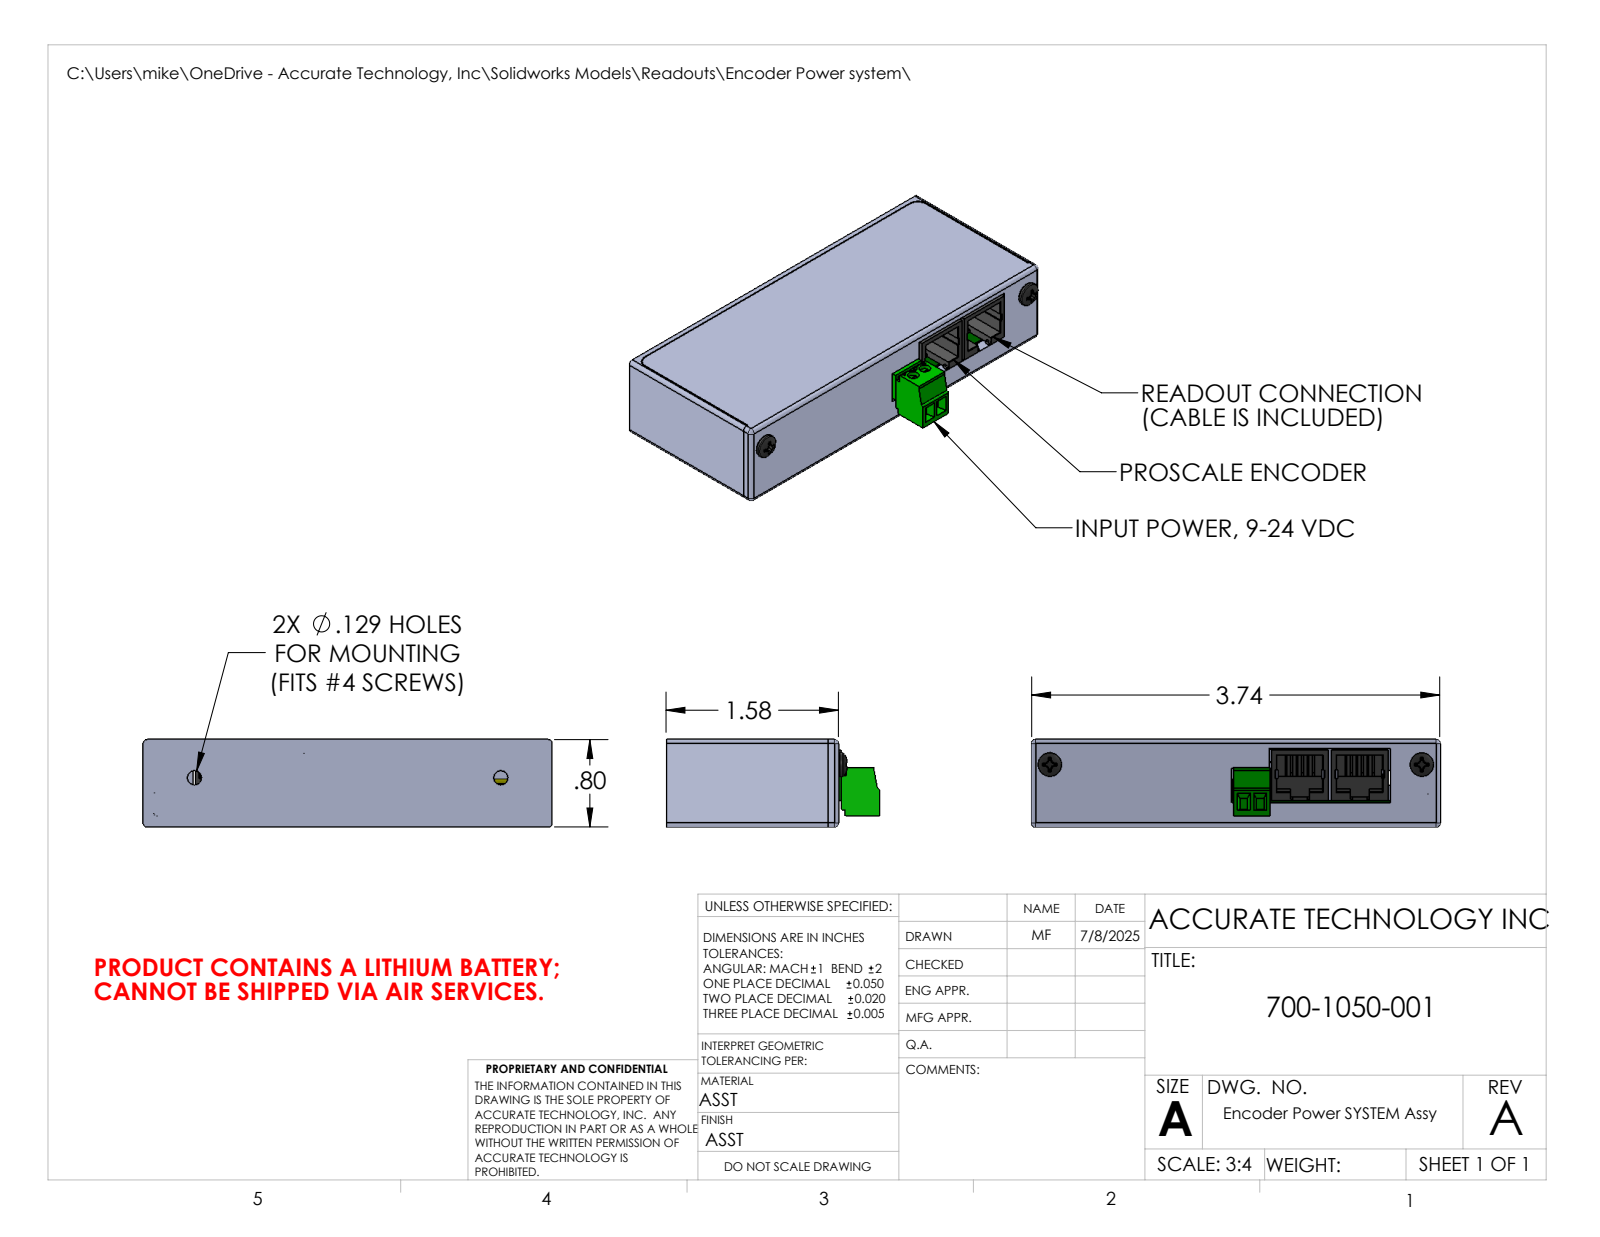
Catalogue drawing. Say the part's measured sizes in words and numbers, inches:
The part is named "Encoder plug; Encoder Power SYSTEM Assy; Encoder Power Board; Charging LED (+7 more)". Its 3-D file was written by "SolidWorks 2024 (AUTOMOTIVE_DESIGN)". It is 11 solids with 1084 faces: 751 planar, 233 cylindrical and 100 other. Overall it measures 3.74 by 1.954 by 0.8 inches. Its volume is 2.607 cubic inches and its surface area 63.45 square inches. Round holes: 4 of diameter 0.128, 2 of diameter 0.083, 2 of diameter 0.089, 2 of diameter 0.106. Round bosses or shafts: 2 of diameter 0.219, 2 of diameter 0.071, 2 of diameter 0.067. Partial cylindrical surfaces (rounded edges, fillets, slot ends): 27 of radius 0.008, 22 of radius 0.04, 18 of radius 0.03, 11 of radius 0.012, 8 of radius 0.005, 8 of radius 0.009, 7 of radius 0.02, 4 of radius 0.012. The main face-to-face distances are 0.1, 0.62, 0.08, 0.242, 0.8, 0.558, 0.478, 0.18, 0.062, 0.54. The hole center spacings are 0.15, 0.323, 3.102, 1.181, 1.331, 1.475, 1.493, 1.624.
